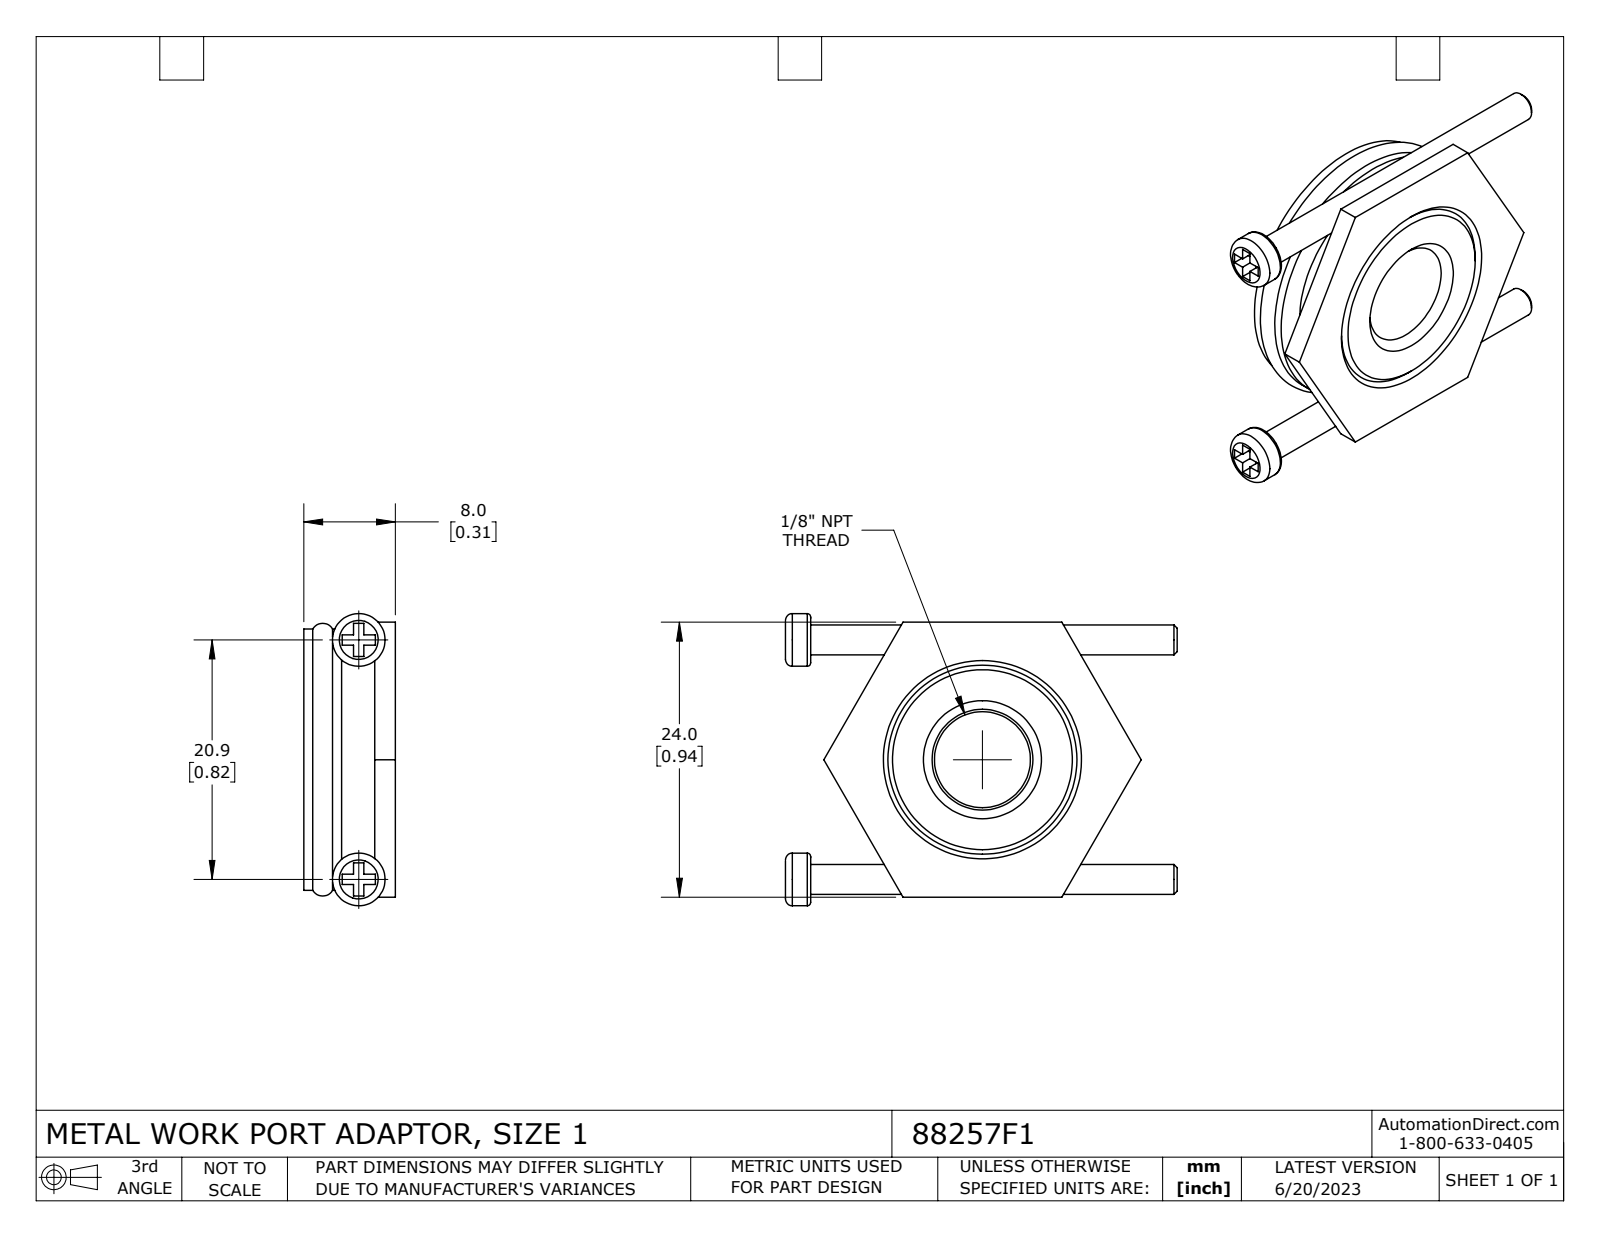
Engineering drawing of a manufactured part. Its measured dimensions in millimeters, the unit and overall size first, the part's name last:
Units: millimetres
Overall size (bounding box): 34.2 × 25.5 × 8
Round bosses / shafts (diameter × count): ⌀4.6 ×2, ⌀2.6 ×2, ⌀22.8 ×1, ⌀18.2 ×1
Main face-to-face distances: 8, 6.2, 1.8, 2.9, 3.3, 4.7, 24, 0.9, 1, 1.9
Volume: 2 950 mm³ · Surface area: 2 650 mm²
Bodies: 3 solids, 83 faces (43 planar, 14 cylindrical, 26 other)
Part name (STEP PRODUCT): 88257F1
STEP written by: SolidWorks 2021 (CONFIG_CONTROL_DESIGN)
